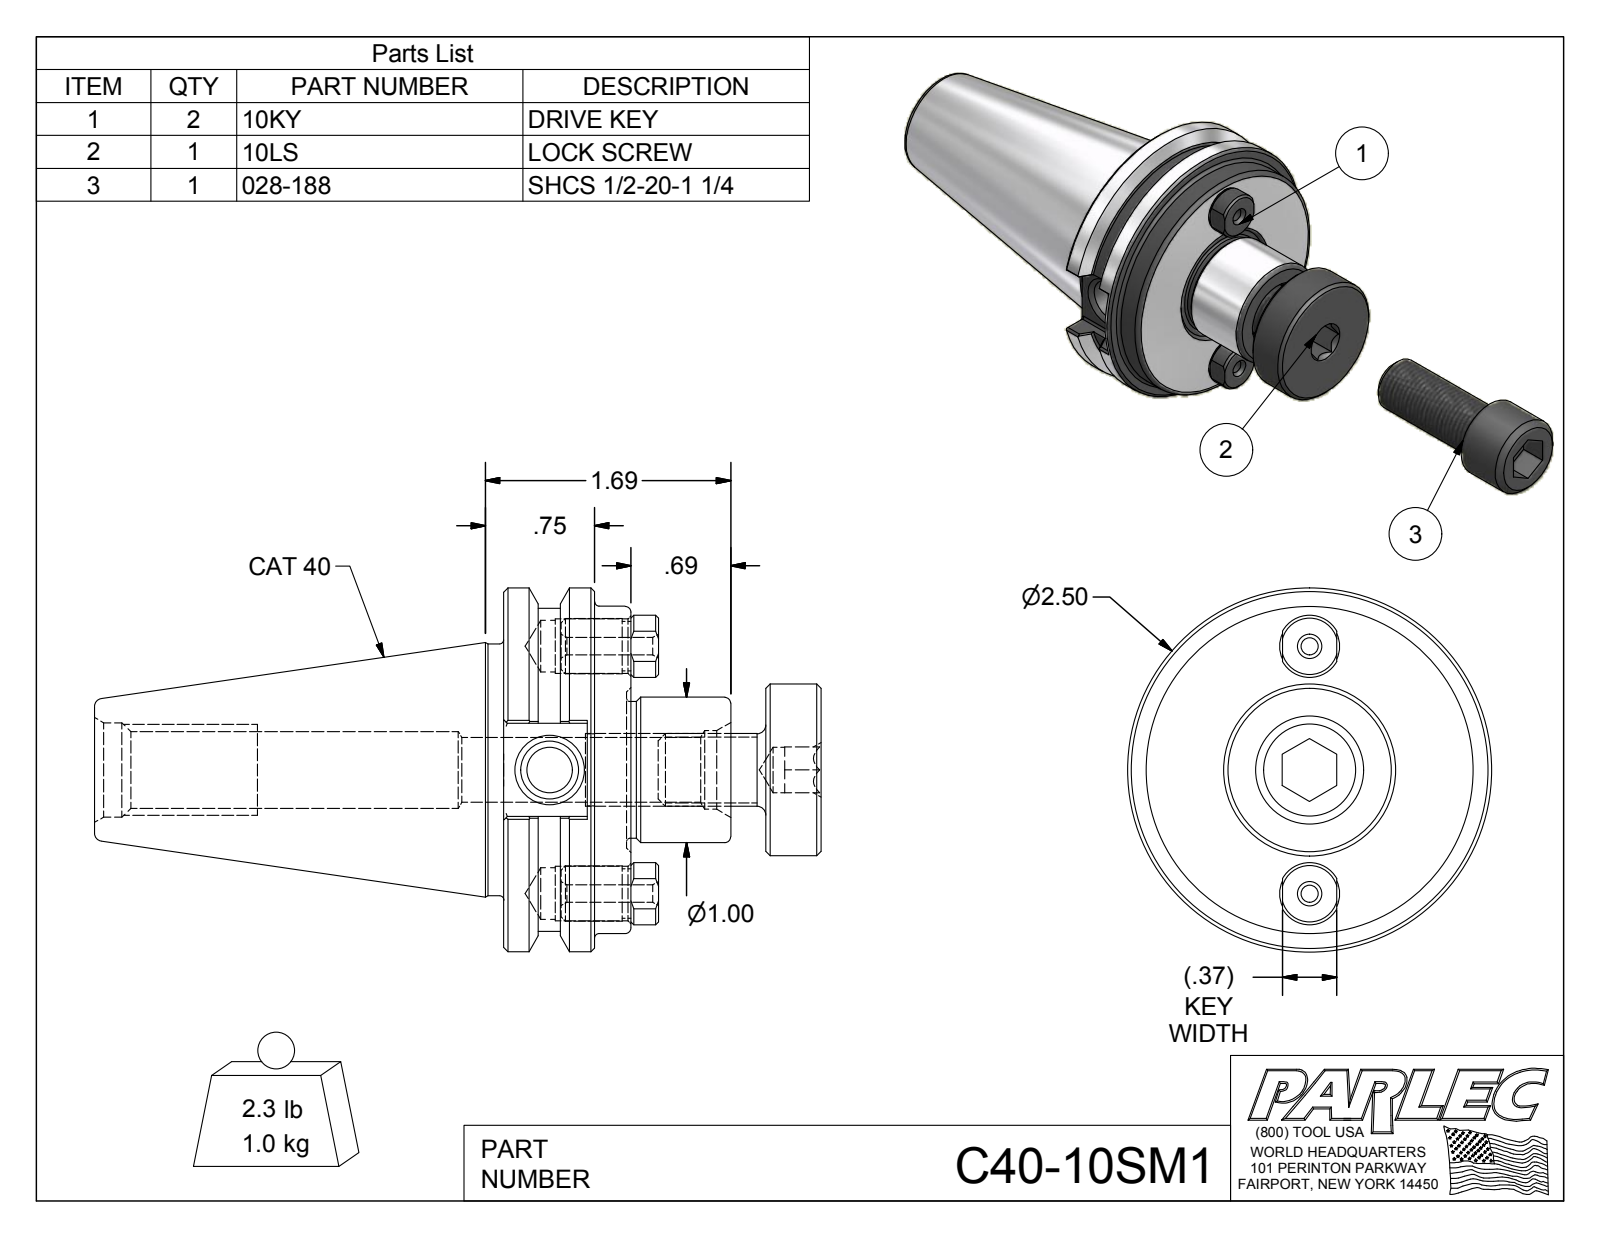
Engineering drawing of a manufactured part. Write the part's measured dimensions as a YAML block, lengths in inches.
part_name: "C40-10SM1; C40-10SM1-1; 10KY; 028-188 (+1 more)"
step_written_by: "Autodesk Inventor 2012 (AUTOMOTIVE_DESIGN)"
units: inches
bodies: {solids: 5, faces: 167, planar: 66, cylindrical: 43, other: 58}
overall_size: [7.62, 2.5, 2.5]
volume: 8.504
surface_area: 50.23
round_holes:
  - {diameter: 0.12, count: 2}
  - {diameter: 0.354, count: 2}
  - {diameter: 0.374, count: 2}
  - {diameter: 0.312, count: 1}
  - {diameter: 0.315, count: 1}
  - {diameter: 0.399, count: 1}
  - {diameter: 0.446, count: 1}
  - {diameter: 0.527, count: 1}
  - {diameter: 0.54, count: 1}
  - {diameter: 0.648, count: 1}
round_bosses_or_shafts:
  - {diameter: 0.38, count: 2}
  - {diameter: 0.34, count: 2}
  - {diameter: 2.5, count: 1}
  - {diameter: 2.25, count: 1}
  - {diameter: 2.219, count: 1}
  - {diameter: 1.73, count: 1}
  - {diameter: 1.18, count: 1}
  - {diameter: 1, count: 1}
partial_cylinders:
  - {radius: 0.02, count: 8}
  - {radius: 0.214, count: 2}
  - {radius: 0.922, count: 1}
face_to_face_distances: [0.875, 2.182, 1.307, 1.802, 0.927, 0.38, 0.25, 0.625, 1.177, 1.557]
hole_center_spacings: [0.85, 1.7]
